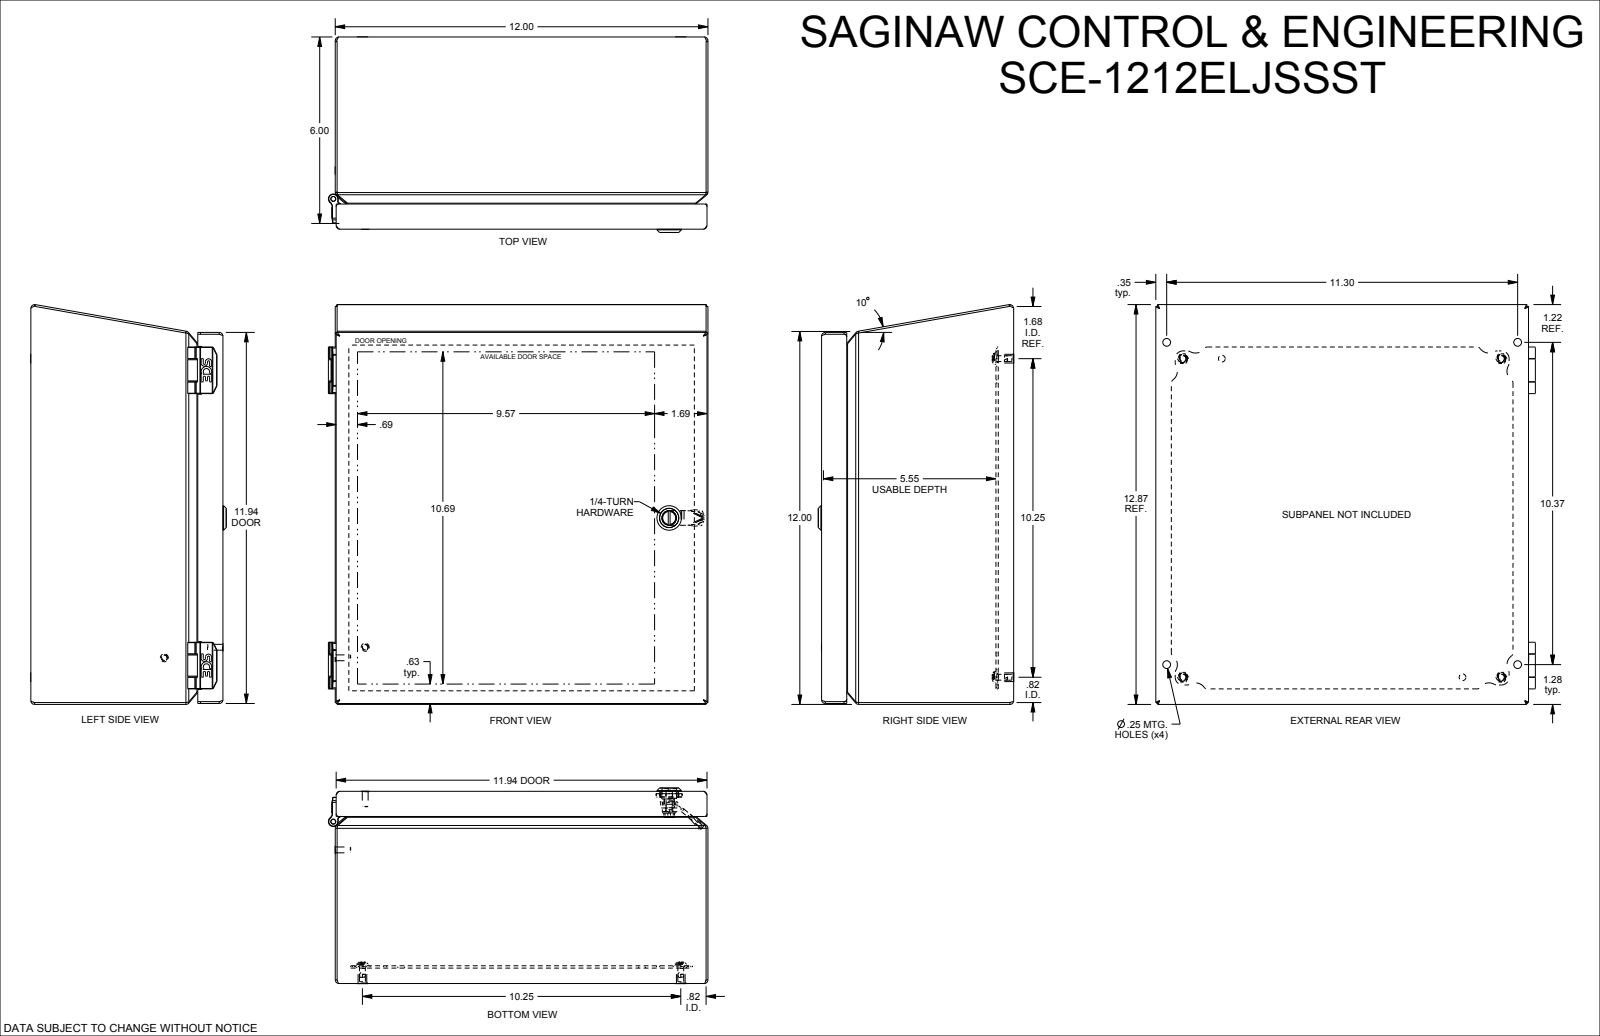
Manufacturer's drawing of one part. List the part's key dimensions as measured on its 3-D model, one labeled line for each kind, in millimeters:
Part name (STEP PRODUCT): SCE-1212ELJSSST
STEP written by: SolidWorks 2021 (AUTOMOTIVE_DESIGN)
Units: millimetres
Bodies: 34 solids, 1454 faces (566 planar, 353 cylindrical, 535 other)
Overall size (bounding box): 326.7 × 310.4 × 159.9
Volume: 818 700 mm³ · Surface area: 1 014 000 mm²
Round holes (diameter × count): ⌀4.1 ×4, ⌀4.8 ×4, ⌀6.4 ×4, ⌀7.2 ×4, ⌀0.5 ×2, ⌀2.5 ×2, ⌀5.5 ×2, ⌀6.8 ×2, ⌀4 ×1, ⌀5 ×1, ⌀5.1 ×1, ⌀6.1 ×1
Round bosses / shafts (diameter × count): ⌀4.8 ×6, ⌀12.3 ×4, ⌀9.5 ×4, ⌀7.1 ×4, ⌀6 ×4, ⌀4.1 ×4, ⌀6.6 ×2, ⌀6.5 ×2
Partial cylindrical surfaces — rounded edges, fillets, slot ends (radius × count): R0.8 ×50, R0.2 ×24, R0.3 ×21, R6.4 ×13, R3.2 ×11, R0.3 ×10, R1.5 ×10, R8.7 ×8
Main face-to-face distances: 1.5, 1.5, 157.1, 155.6, 155.6, 154.1, 303.3, 14.5, 13, 141.1
Hole centre spacings: 241.3, 260.4, 274, 0.5, 16.8, 18.9, 31.8, 130.5
